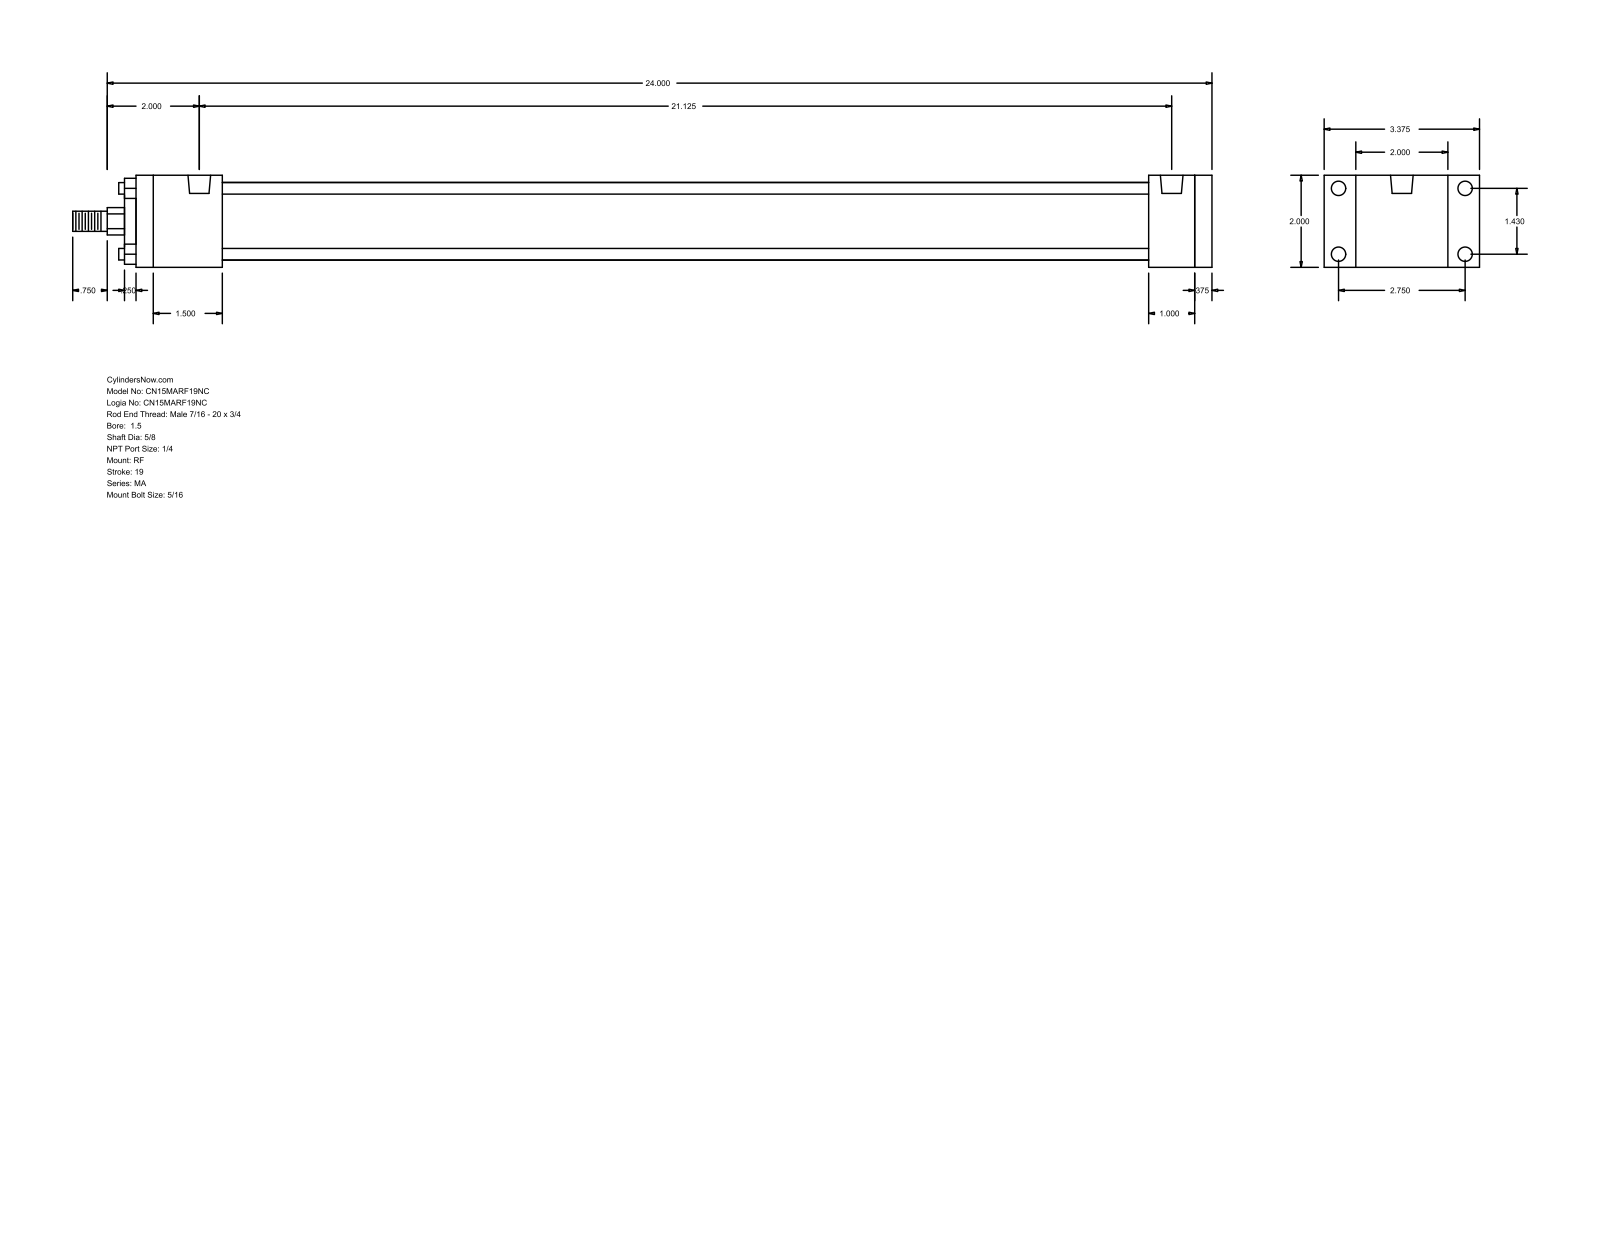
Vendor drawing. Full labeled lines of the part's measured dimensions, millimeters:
Part name (STEP PRODUCT): MA_RF__0150_0.625
STEP written by: GSSL Pune (CONFIG_CONTROL_DESIGN)
Units: millimetres
Bodies: 0 solids, 92 faces (64 planar, 28 cylindrical, 0 other)
Overall size (bounding box): 628.65 × 85.72 × 50.8
Round holes (diameter × count): ⌀7.94 ×8, ⌀12.49 ×2
Round bosses / shafts (diameter × count): ⌀6.35 ×4, ⌀42.93 ×1, ⌀28.57 ×1, ⌀15.88 ×1, ⌀11.11 ×1
Partial cylindrical surfaces — rounded edges, fillets, slot ends (radius × count): R7.54 ×1
Main face-to-face distances: 50.8, 593.72, 9.52, 584.2, 34.93, 558.79, 25.41, 47.62, 511.17, 536.58
Hole centre spacings: 36.32, 69.84, 78.72, 536.58
